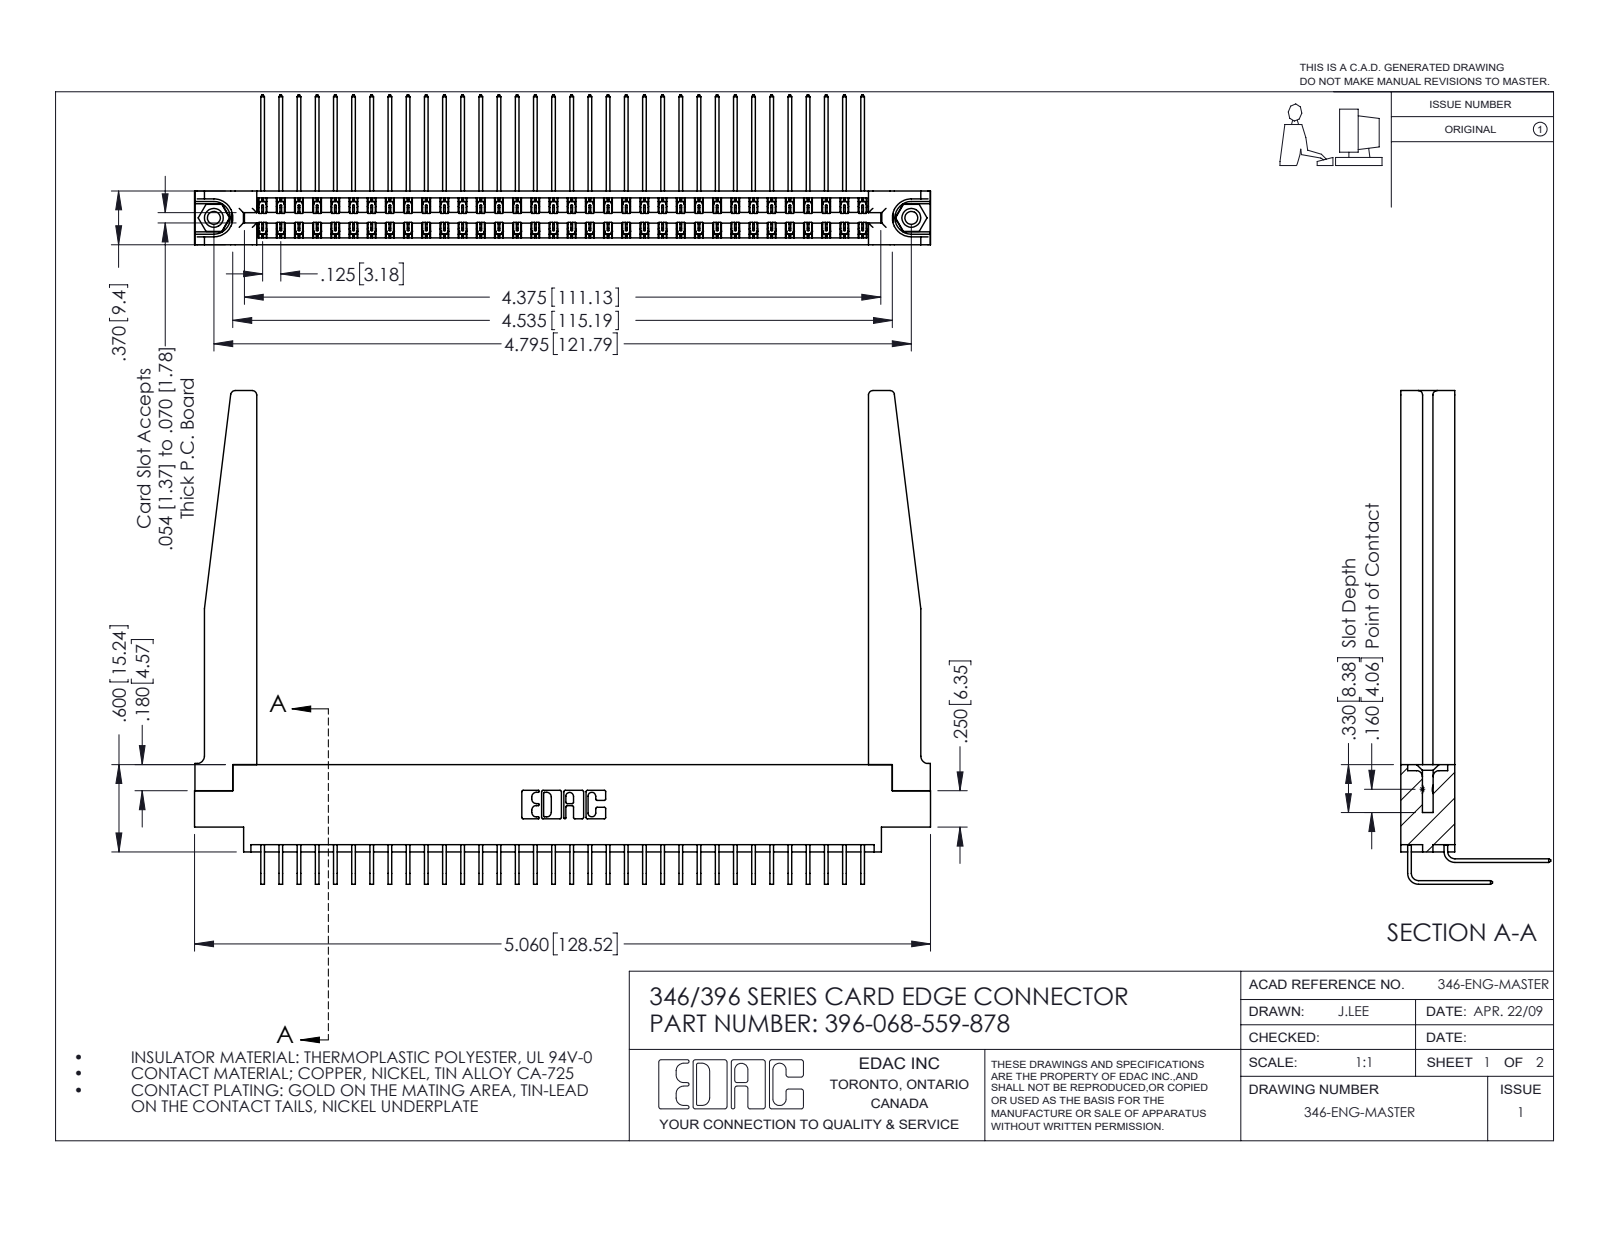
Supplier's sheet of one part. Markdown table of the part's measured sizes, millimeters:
| quantity | value |
| --- | --- |
| part name | 345-292-001_558 559 Tail - 1; 396-068-559-878; 346 Part_0.170 Offset - 0.156 Dia-TH; 345-250-001_345-250-001-102 (+2 more) |
| STEP written by | SolidWorks 2016 (CONFIG_CONTROL_DESIGN) |
| units | millimeters |
| bodies | 73 solids, 4032 faces (2738 planar, 1242 cylindrical, 52 other) |
| overall size | 128.5 × 86.2 × 26.2 |
| volume | 19 620 mm³ |
| surface area | 25 940 mm² |
| round holes (diameter × count) | 2.3 × 2, 3.2 × 2, 4 × 2, 1.6 × 1 |
| round bosses / shafts (diameter × count) | 3.9 × 2 |
| partial cylindrical surfaces (radius × count) | 0.2 × 102, 0.3 × 22, 0.8 × 8, 0.2 × 6, 0.8 × 6, 1.3 × 4, 0.7 × 3, 0.4 × 2 |
| main face-to-face distances | 9.4, 1.2, 8.2, 1.8, 0.6, 3.8, 3.8, 6.4, 7.6, 7 |
| hole center spacings | 6.2, 116.5, 121.8 |
